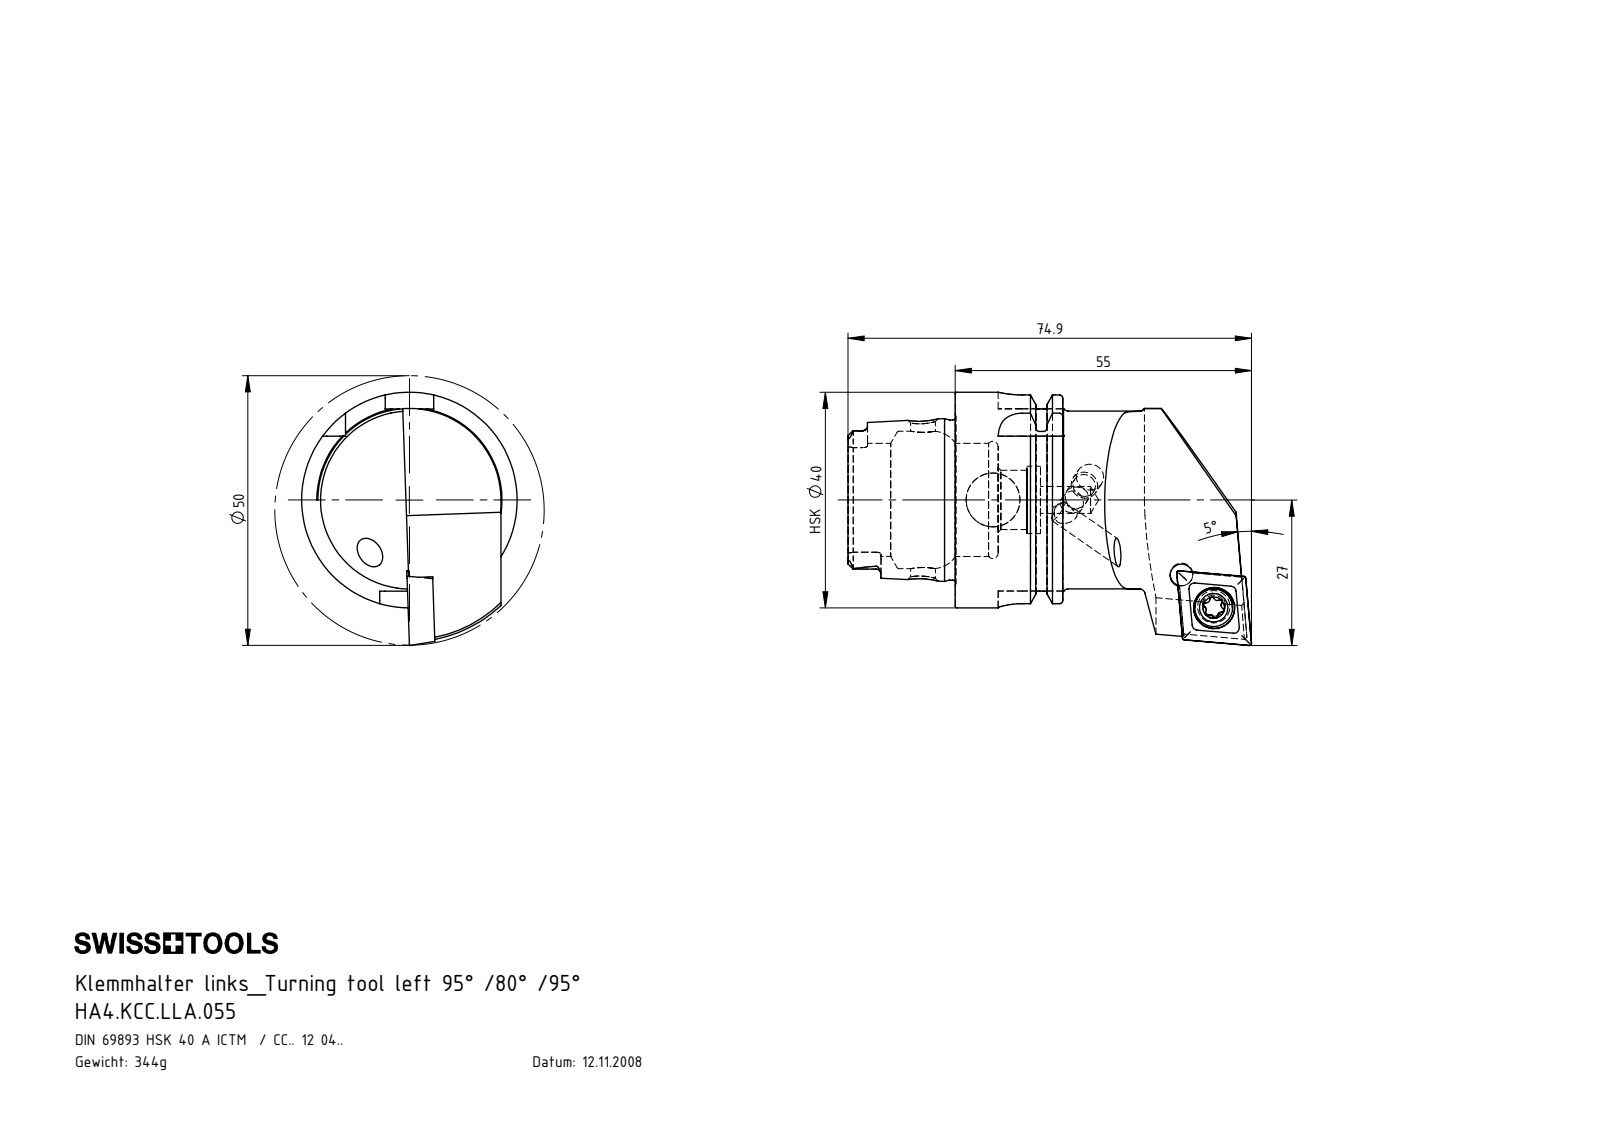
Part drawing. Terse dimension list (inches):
name: HA4-KCC.LLA.055; KVT_MB_600_050; CCMT120404; WCC-ER2.001.010_A (+1 more)
written by: SolidWorks 2012 (CONFIG_CONTROL_DESIGN)
unit: in
bodies: 5 solids, 305 faces (75 planar, 92 cylindrical, 138 other)
size: 2.949 × 1.85 × 1.575
volume: 2.684 in³; area: 22.55 in²
holes: 4× ⌀0.165, 2× ⌀0.197, 1× ⌀0.157, 1× ⌀0.181, 1× ⌀0.217, 1× ⌀0.299, 1× ⌀0.394, 1× ⌀0.433, 1× ⌀0.492, 1× ⌀0.827, 1× ⌀1.004
bosses: 2× ⌀0.197, 1× ⌀1.575, 1× ⌀1.368, 1× ⌀1.299, 1× ⌀1.17, 1× ⌀0.276
rounds: 6× R0.015, 6× R0.035, 4× R0.177, 3× R0.027, 3× R0.027, 2× R0.072, 2× R0.074, 1× R0.157
face distances: 0.313, 0.785, 0.472, 0.783, 1.096, 1.569, 0.175, 1.406, 0.622, 0.309
hole spacings: 0.333, 0.338
